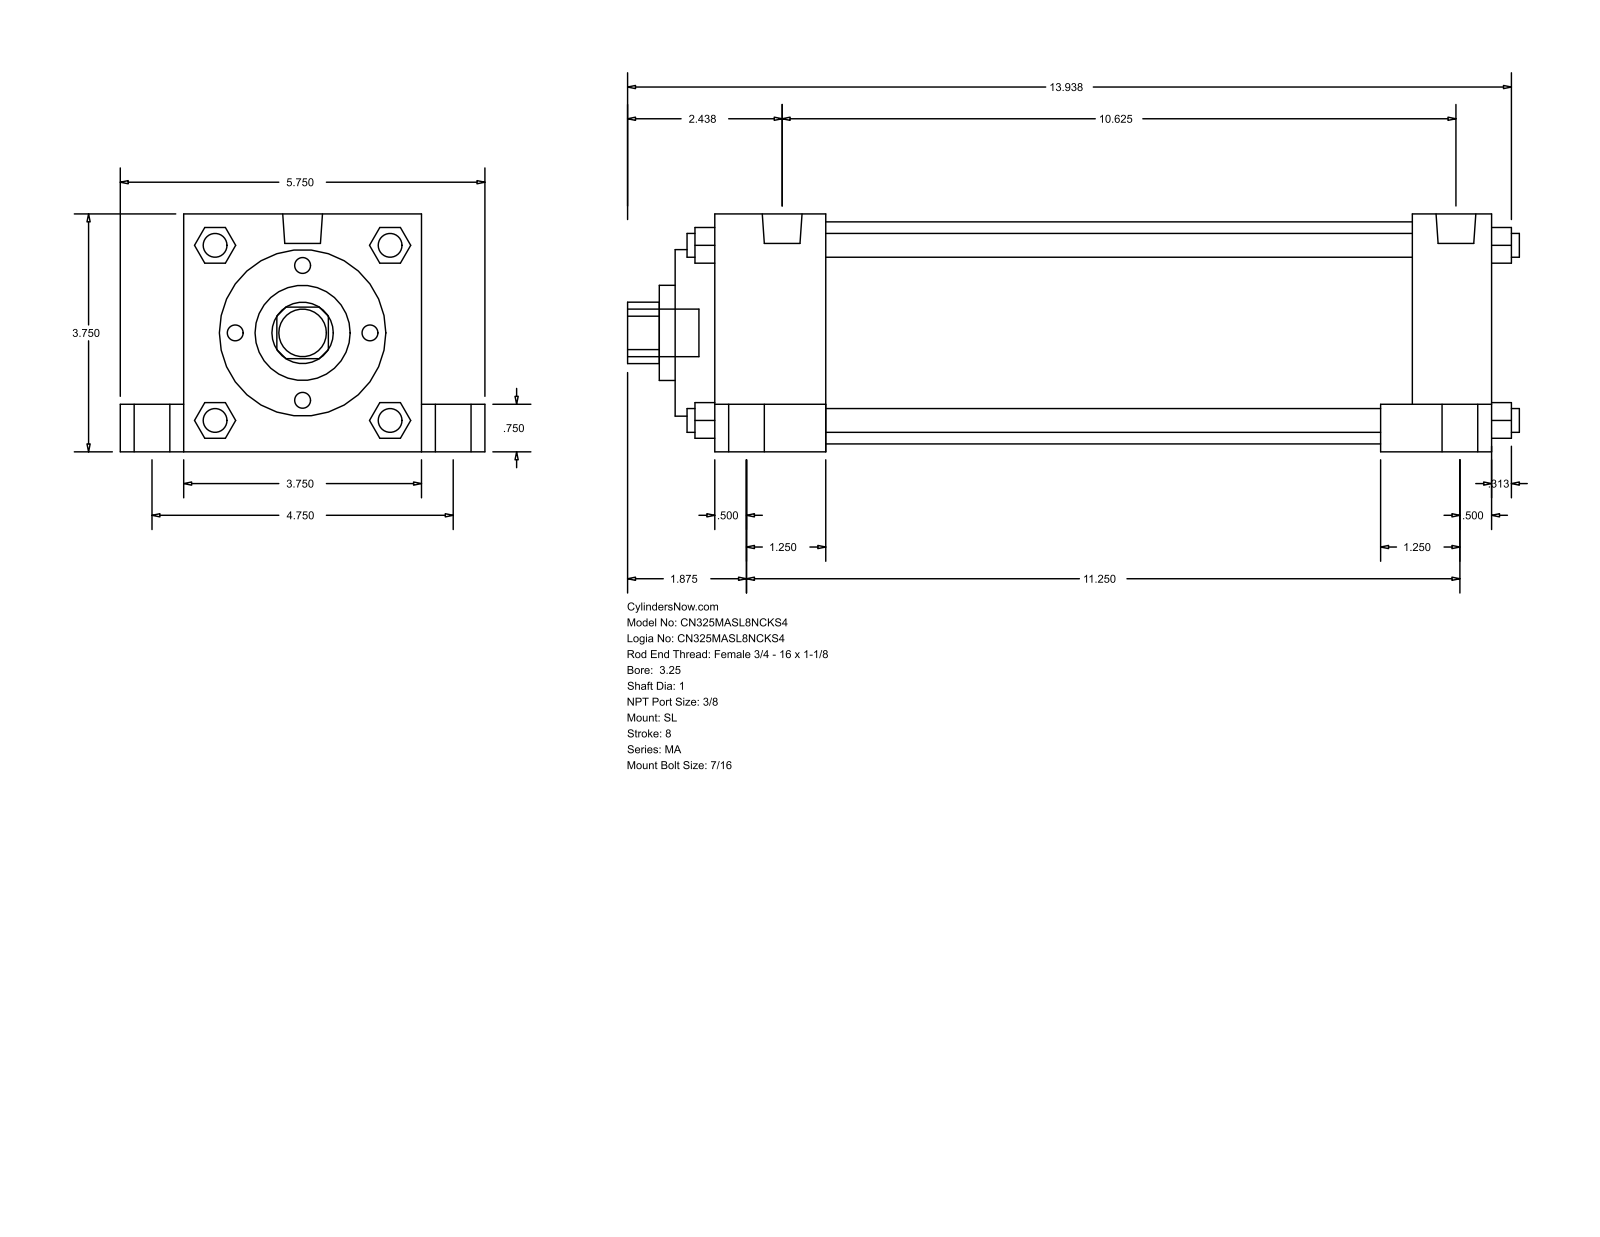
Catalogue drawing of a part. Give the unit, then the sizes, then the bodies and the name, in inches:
Units: inches
Overall size (bounding box): 14.063 × 5.75 × 3.75
Round holes (diameter × count): ⌀1 ×1, ⌀1.5 ×1, ⌀2.625 ×1, ⌀3.5 ×1
Round bosses / shafts (diameter × count): ⌀0.813 ×4, ⌀0.563 ×4, ⌀0.437 ×4, ⌀0.375 ×4, ⌀0.627 ×2, ⌀0.75 ×1
Partial cylindrical surfaces — rounded edges, fillets, slot ends (radius × count): R0.484 ×1
Main face-to-face distances: 3.75, 12.25, 0.625, 1, 4.75, 12.875, 0.75, 11, 1.25, 1.75
Bodies: 0 solids, 150 faces (113 planar, 37 cylindrical, 0 other)
Part name (STEP PRODUCT): MA_SL__0325_1
STEP written by: GSSL Pune (CONFIG_CONTROL_DESIGN)
